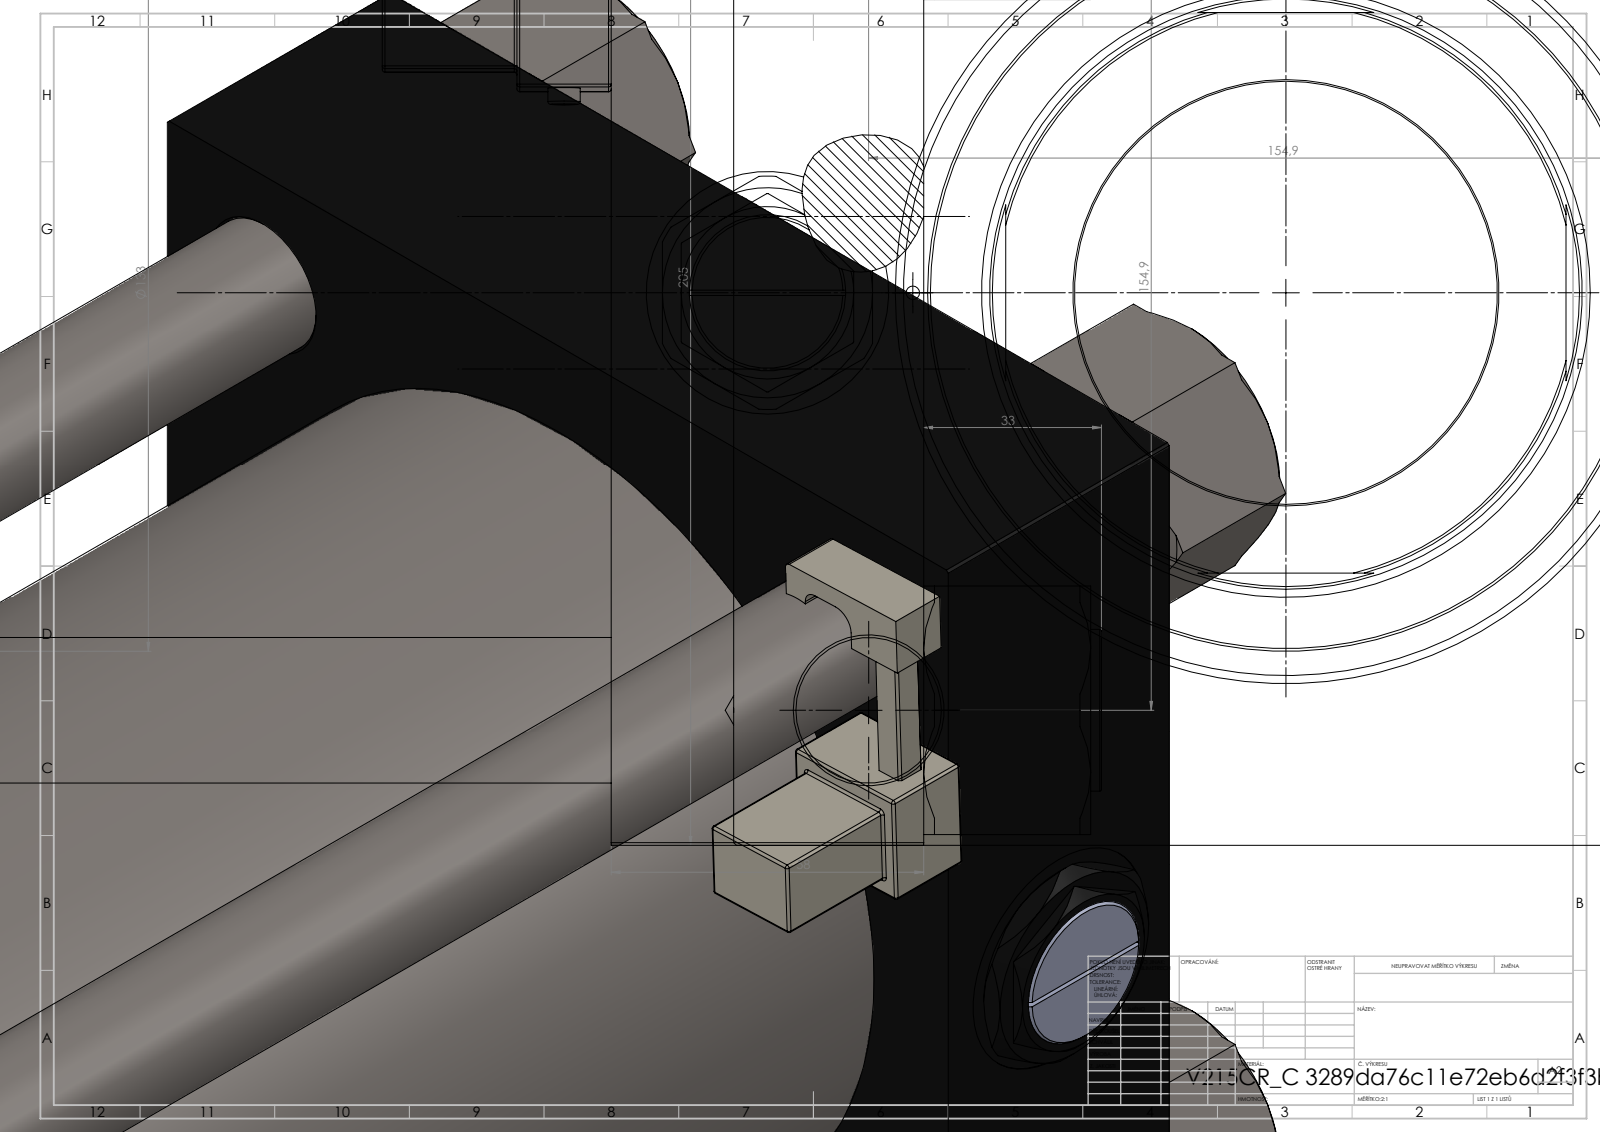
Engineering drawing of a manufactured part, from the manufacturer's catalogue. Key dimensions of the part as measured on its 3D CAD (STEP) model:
Part name (STEP PRODUCT): V215CR_MSU; V215CR_VCP_C; NUT_M5_C; Zatka_pro_OIL_PORT (+3 more)
STEP written by: SolidWorks 2019 (CONFIG_CONTROL_DESIGN)
Units: millimetres
Bodies: 13 solids, 1333 faces (629 planar, 128 cylindrical, 576 other)
Overall size (bounding box): 526 × 213.57 × 205
Volume: 10 730 000 mm³ · Surface area: 1 126 000 mm²
Round holes (diameter × count): ⌀27 ×4, ⌀2.5 ×2, ⌀7 ×2, ⌀33.24 ×2, ⌀45 ×2, ⌀78.5 ×1, ⌀110 ×1, ⌀113 ×1, ⌀120 ×1, ⌀142 ×1, ⌀160 ×1
Round bosses / shafts (diameter × count): ⌀30 ×4, ⌀166 ×1, ⌀133 ×1, ⌀6 ×1
Partial cylindrical surfaces — rounded edges, fillets, slot ends (radius × count): R0.5 ×24, R1 ×1, R2.5 ×1, R4 ×1, R54 ×1
Main face-to-face distances: 205, 58, 380, 322, 461, 403, 81, 432.3, 374.3, 52.3
Hole centre spacings: 77.88, 109.53, 154.9, 165.89, 69.25, 219.06, 138.5, 378
